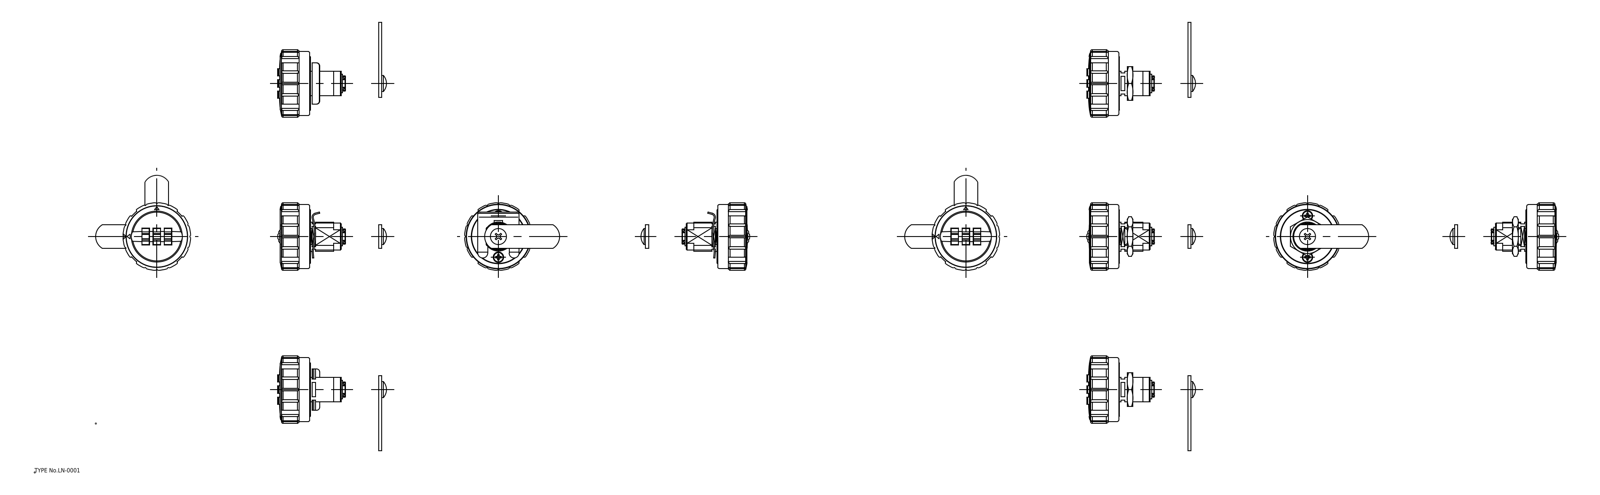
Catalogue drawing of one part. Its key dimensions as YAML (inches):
part_name: "cover; nut; knob; retainer"
step_written_by: "spGate 19.8.4 (****-****-****-****) (AUTOMOTIVE_DESIGN)"
units: inches
bodies: {solids: 6, faces: 616, planar: 322, cylindrical: 190, other: 104}
overall_size: [7.808, 2.444, 1.739]
volume: 3.421
surface_area: 51.66
round_holes:
  - {diameter: 0.748, count: 1}
  - {diameter: 1.31, count: 1}
  - {diameter: 1.398, count: 1}
  - {diameter: 1.587, count: 1}
round_bosses_or_shafts:
  - {diameter: 1.642, count: 1}
  - {diameter: 1.575, count: 1}
  - {diameter: 0.472, count: 1}
  - {diameter: 0.413, count: 1}
partial_cylinders:
  - {radius: 0.028, count: 12}
  - {radius: 0.004, count: 6}
  - {radius: 0.079, count: 4}
  - {radius: 3.87, count: 4}
  - {radius: 0.071, count: 2}
  - {radius: 0.11, count: 2}
  - {radius: 0.128, count: 2}
  - {radius: 0.28, count: 2}
face_to_face_distances: [5.906, 0.039, 0.378, 5.945, 5.866, 0.418, 6.284, 0.339, 5.527, 0.217]
